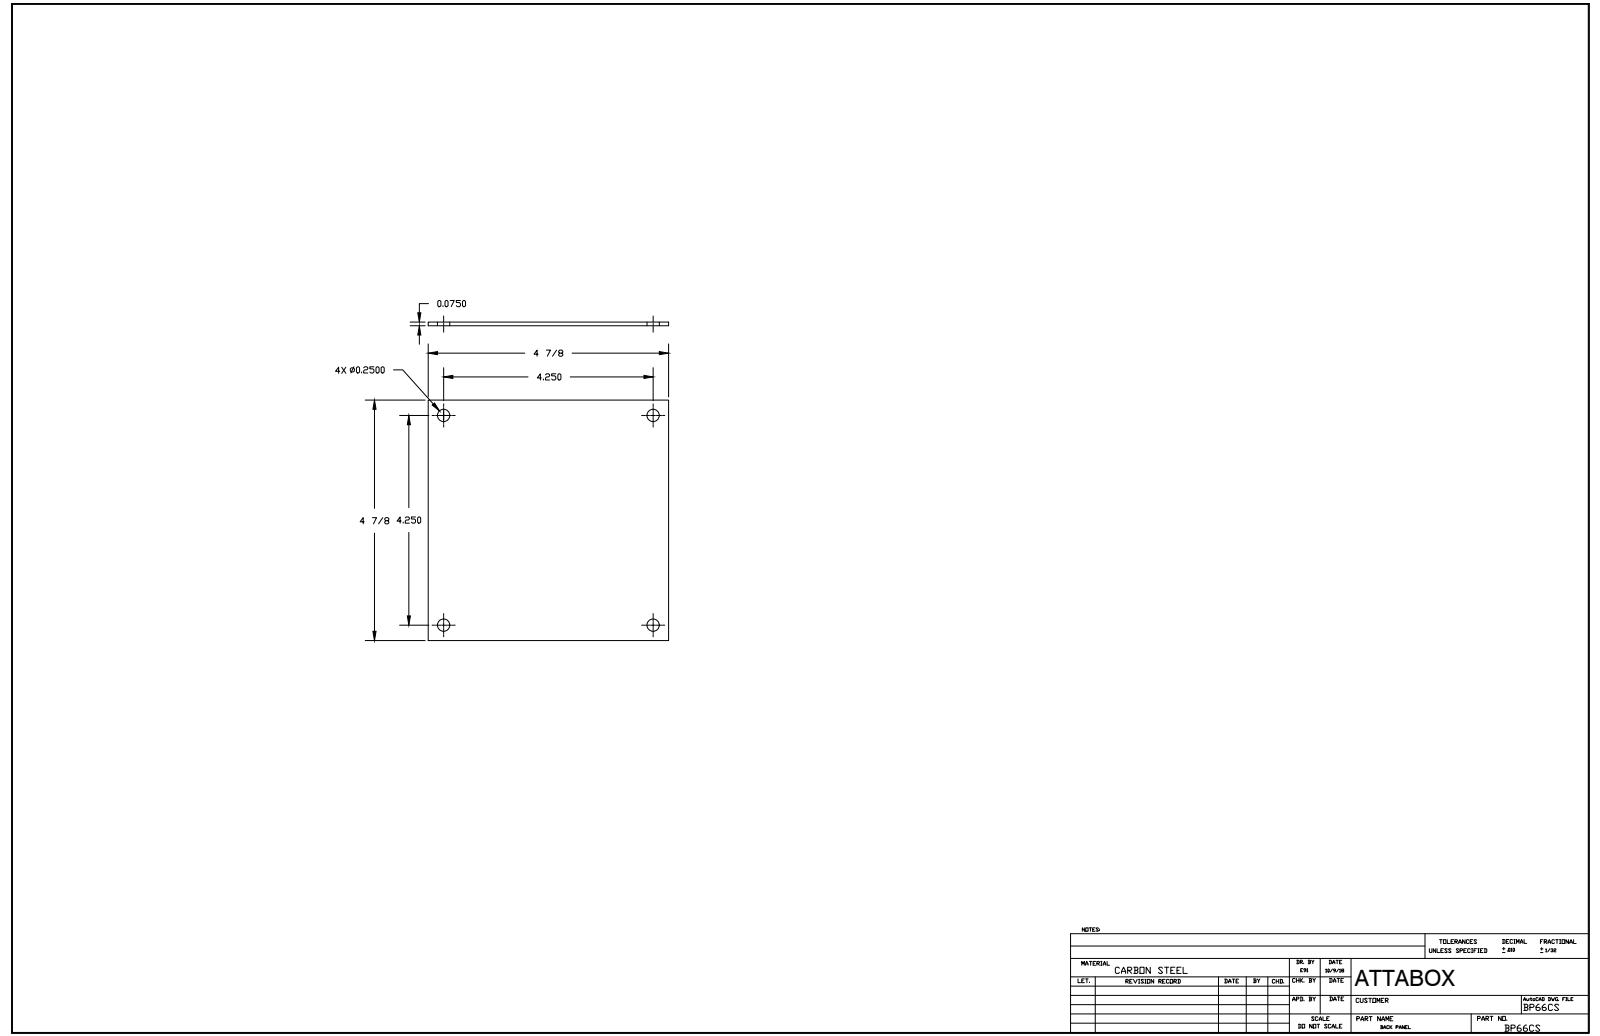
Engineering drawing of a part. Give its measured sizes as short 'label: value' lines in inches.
name: BP66CS_STP
written by: Autodesk Inventor 2014 (AUTOMOTIVE_DESIGN)
unit: in
bodies: 1 solid, 10 faces (6 planar, 4 cylindrical, 0 other)
size: 4.875 × 4.875 × 0.075
volume: 1.768 in³; area: 48.84 in²
holes: 4× ⌀0.25
face distances: 0.075, 4.875
hole spacings: 4.25, 6.01
